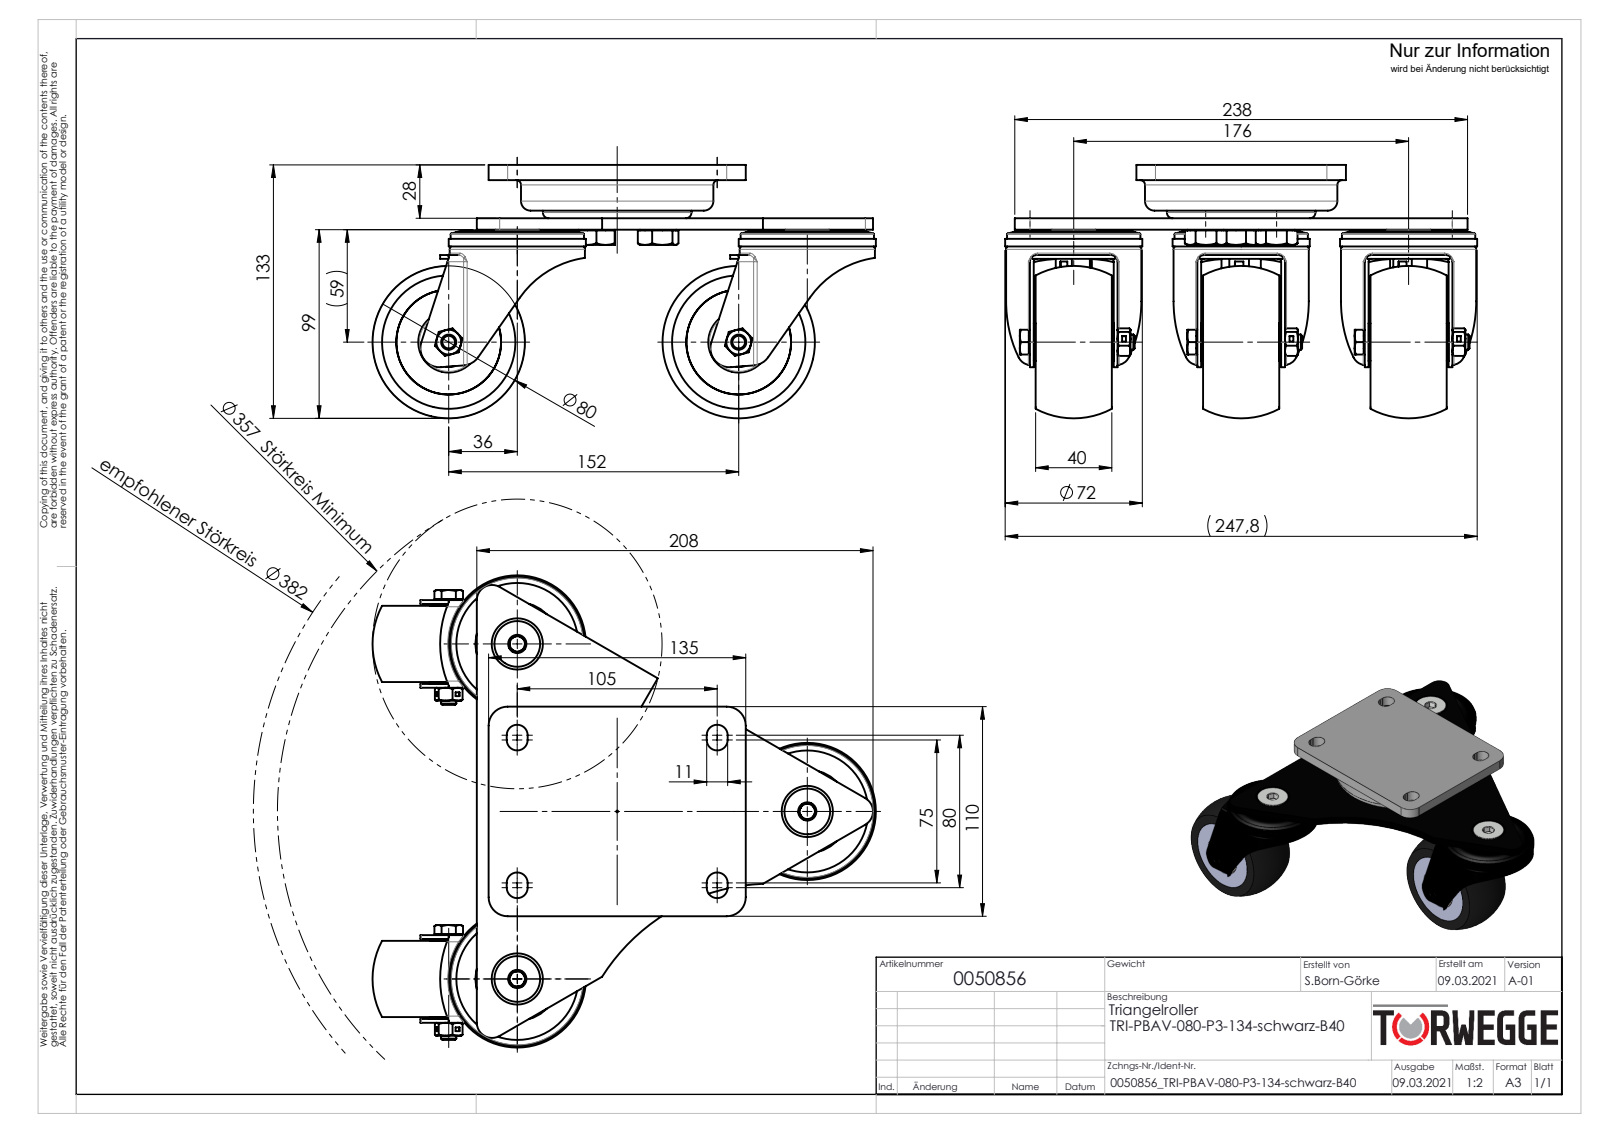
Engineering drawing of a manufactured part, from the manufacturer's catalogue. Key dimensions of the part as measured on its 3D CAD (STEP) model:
Part name (STEP PRODUCT): 0050856
STEP written by: SolidWorks 2020 (AUTOMOTIVE_DESIGN)
Units: millimetres
Bodies: 56 solids, 1217 faces (409 planar, 379 cylindrical, 429 other)
Overall size (bounding box): 259.25 × 247.8 × 131.96
Volume: 1 082 000 mm³ · Surface area: 352 269 mm²
Round holes (diameter × count): ⌀10.2 ×6, ⌀12 ×5, ⌀13 ×3, ⌀67 ×3, ⌀6.8 ×2, ⌀8 ×2, ⌀8.2 ×2, ⌀18 ×2, ⌀26 ×2, ⌀27 ×2, ⌀32 ×2, ⌀55 ×2
Round bosses / shafts (diameter × count): ⌀72 ×3, ⌀71 ×3, ⌀70 ×3, ⌀24 ×3, ⌀19 ×3, ⌀12 ×3, ⌀20 ×2, ⌀13 ×2
Partial cylindrical surfaces — rounded edges, fillets, slot ends (radius × count): R5.5 ×8, R10 ×8, R1.5 ×6, R2.5 ×6, R3.5 ×6, R4.5 ×6, R5 ×3, R6 ×3
Main face-to-face distances: 6, 87.9, 8.3, 14.3, 34, 2, 28, 42.3, 175.8, 40
Hole centre spacings: 37.24, 175.8, 80.86, 112.12, 114.39, 114.86, 78.31, 152.25
